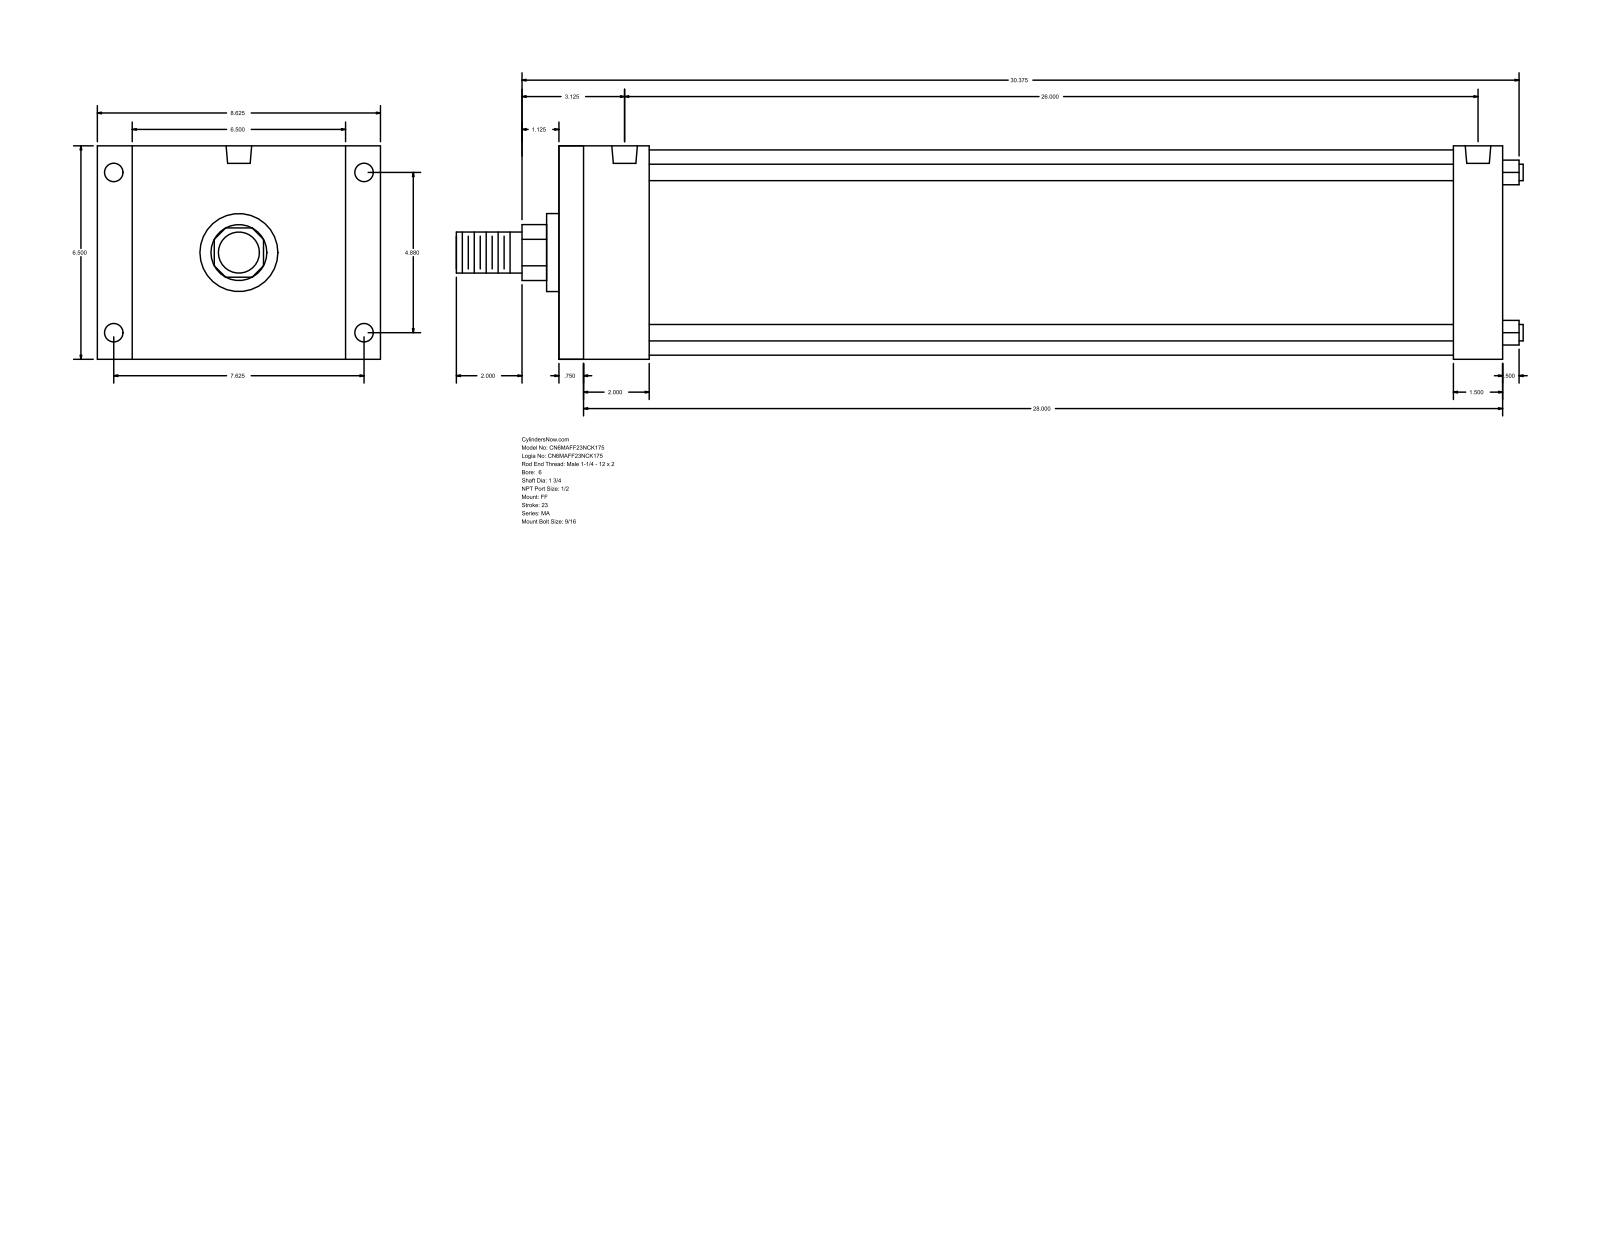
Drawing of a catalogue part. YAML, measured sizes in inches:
part_name: "MA_FF__0600_1.75"
step_written_by: "GSSL Pune (CONFIG_CONTROL_DESIGN)"
units: inches
bodies: {solids: 0, faces: 92, planar: 64, cylindrical: 28, other: 0}
overall_size: [32.5, 8.625, 6.5]
round_holes:
  - {diameter: 0.563, count: 4}
  - {diameter: 0.687, count: 4}
  - {diameter: 0.778, count: 2}
round_bosses_or_shafts:
  - {diameter: 0.5, count: 4}
  - {diameter: 6.25, count: 1}
  - {diameter: 2.375, count: 1}
  - {diameter: 1.75, count: 1}
  - {diameter: 1.25, count: 1}
partial_cylinders:
  - {radius: 0.852, count: 1}
face_to_face_distances: [6.5, 28.75, 0.75, 28, 2.75, 1.5, 2, 26, 27.25, 26.5]
hole_center_spacings: [4.88, 7.625, 9.053, 26]
